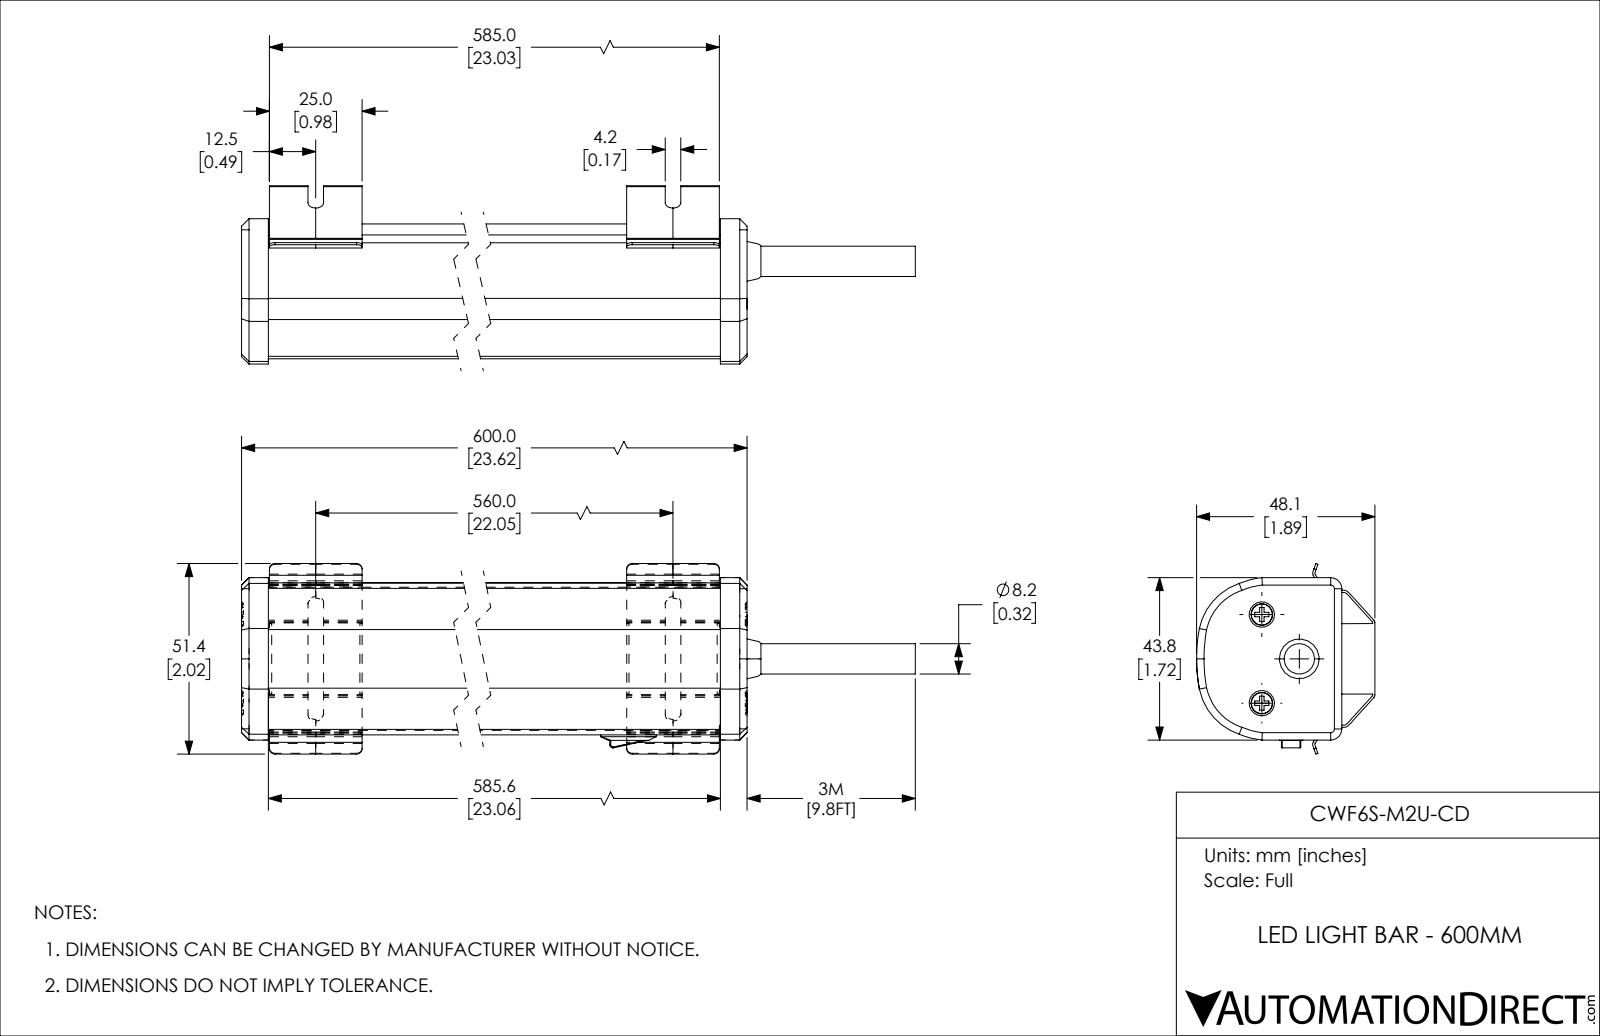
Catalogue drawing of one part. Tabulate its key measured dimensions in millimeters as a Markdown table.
| quantity | value |
| --- | --- |
| part name | CWF6S-M2U-CD |
| STEP written by | SolidWorks 2018 (AUTOMOTIVE_DESIGN) |
| units | millimeters |
| bodies | 3 solids, 283 faces (123 planar, 67 cylindrical, 93 other) |
| overall size | 645.4 × 51.4 × 48.1 |
| volume | 819 400 mm³ |
| surface area | 98 900 mm² |
| round bosses / shafts (diameter × count) | 5.7 × 2, 8.2 × 1 |
| partial cylindrical surfaces (radius × count) | 1.5 × 8, 2.1 × 4, 0.2 × 2, 0.2 × 2, 0.4 × 2, 0.8 × 2, 1 × 2, 15 × 2 |
| main face-to-face distances | 41, 1.2, 39.8, 0.6, 2.1, 38.6, 600, 560, 15.4, 13.3 |
